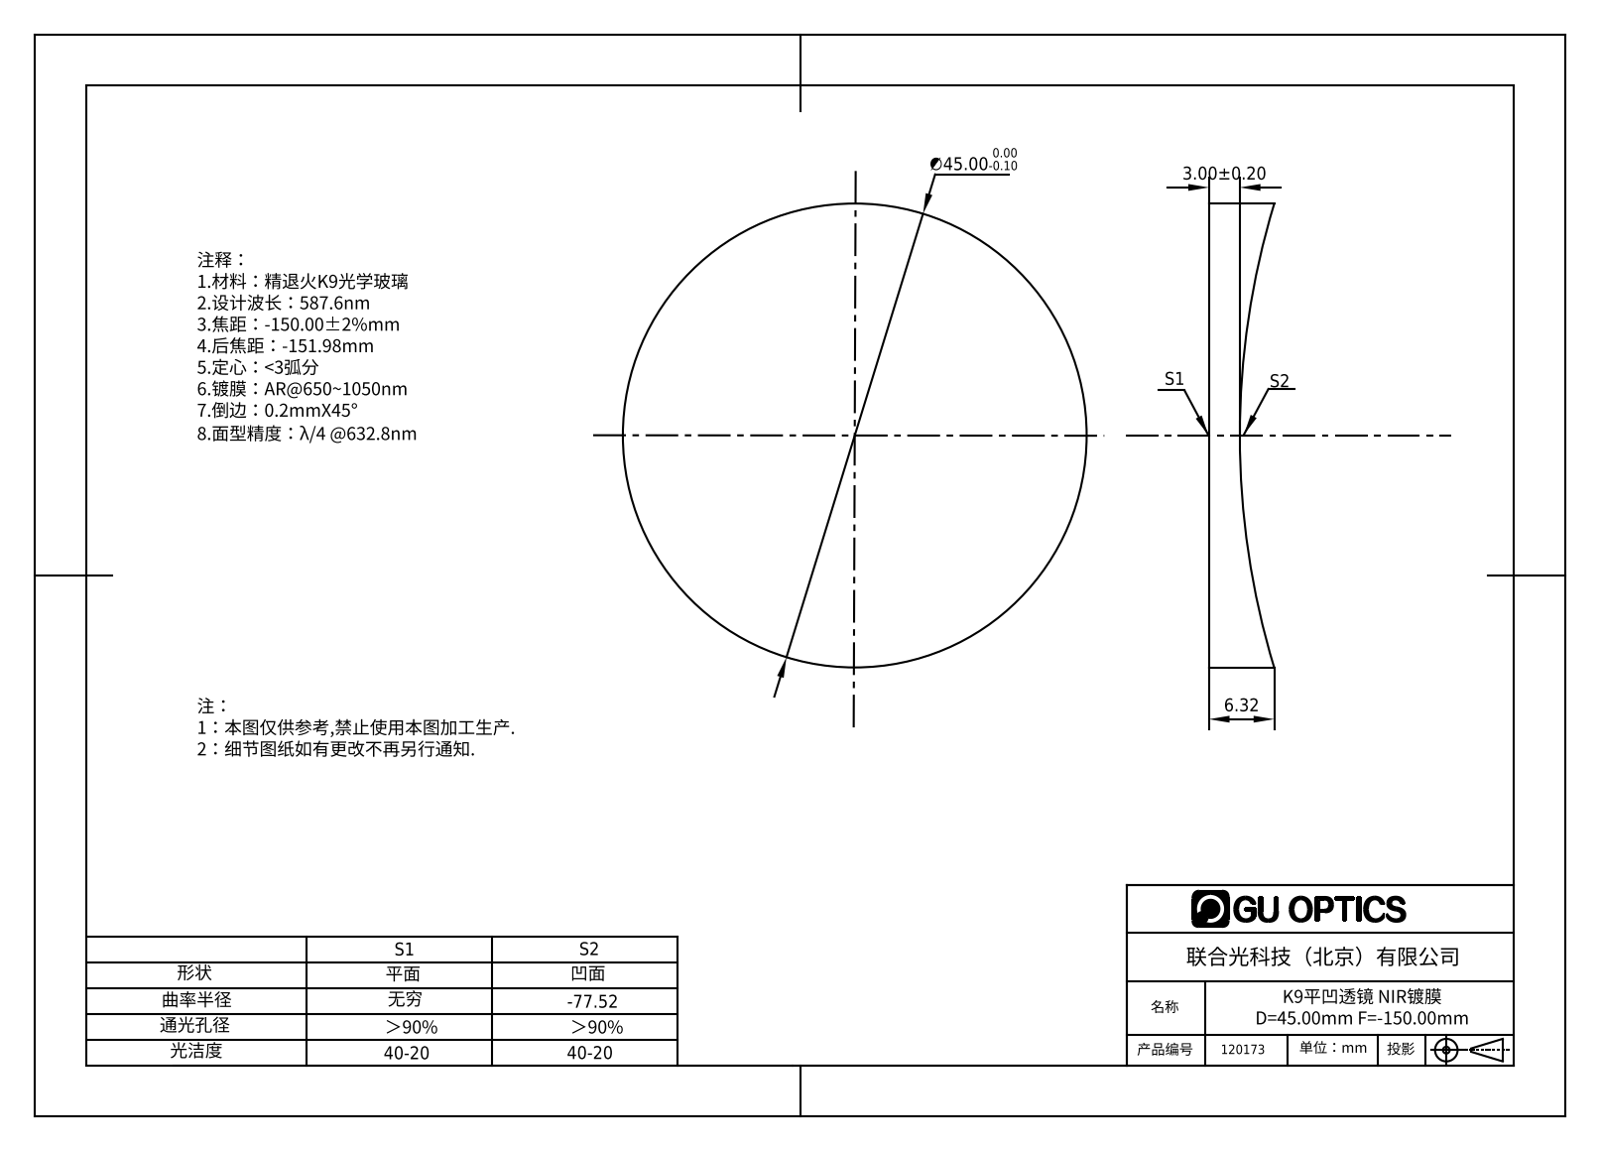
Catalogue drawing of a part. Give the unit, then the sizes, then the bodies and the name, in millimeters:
Units: millimetres
Overall size (bounding box): 45 × 45 × 6.34
Round bosses / shafts (diameter × count): ⌀45 ×1
Volume: 7 406 mm³ · Surface area: 4 112 mm²
Bodies: 1 solid, 5 faces (1 planar, 2 cylindrical, 2 other)
Part name (STEP PRODUCT): 120053
STEP written by: SolidWorks 2016 (AUTOMOTIVE_DESIGN)
